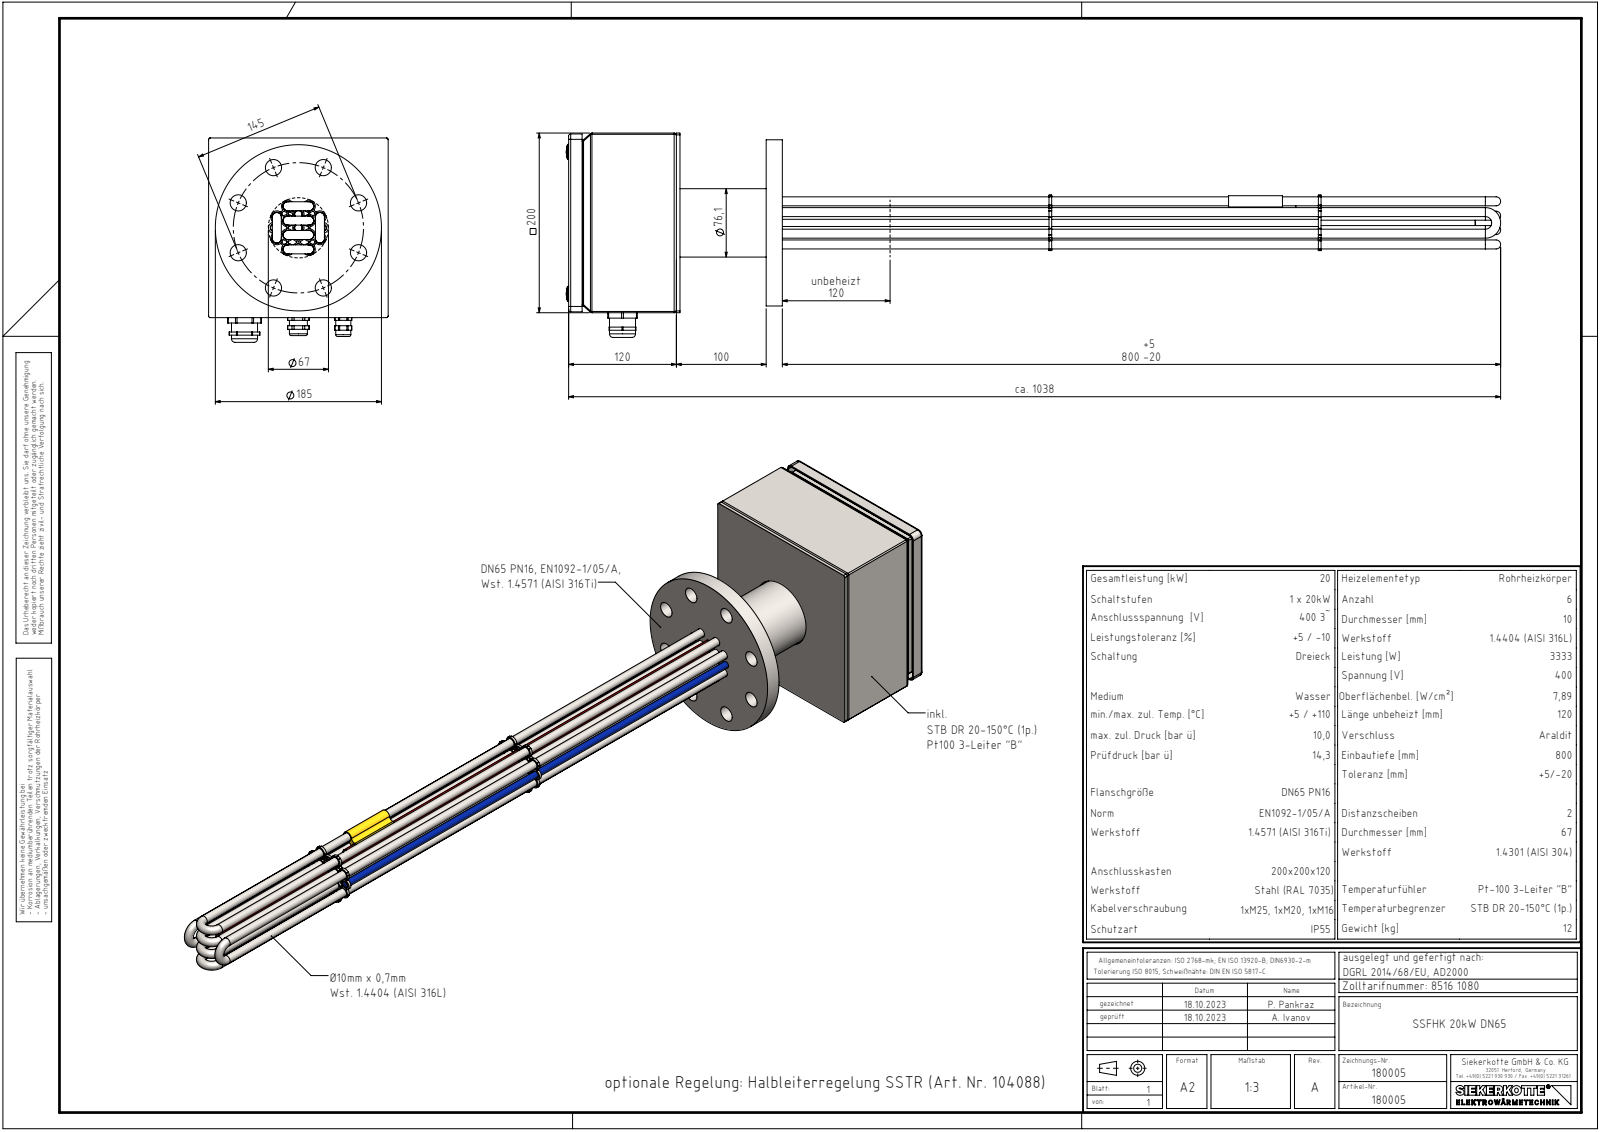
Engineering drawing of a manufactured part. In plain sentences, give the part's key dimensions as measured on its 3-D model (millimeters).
The part is named "BODY^AK 200x200x120_Anschlusskasten_SSFHK; Anschlusskasten^SSFHK_200x200x120; WB 10er^Fühlerschutzrohre_SSFHK; Kühlstrecke^SSFHK_DN80 (+8 more)". Its 3-D file was written by "SolidWorks 2021 (AUTOMOTIVE_DESIGN)". It is 31 solids with 1686 faces: 428 planar, 954 cylindrical and 304 other. Overall it measures 1040.75 by 227.5 by 200 millimeters. Its volume is 1 275 000 cubic millimeters and its surface area 1 234 000 square millimeters. Round holes: 16 of diameter 10.2, 12 of diameter 5, 12 of diameter 8, 12 of diameter 10.7, 9 of diameter 18, 4 of diameter 8.4, 4 of diameter 8.7, 3 of diameter 8.5, 2 of diameter 7, 2 of diameter 9.2, 2 of diameter 9.7, 1 of diameter 6.2. Round bosses or shafts: 16 of diameter 10, 6 of diameter 8, 4 of diameter 9.4, 4 of diameter 5.3, 4 of diameter 5, 4 of diameter 4.3, 4 of diameter 2.7, 2 of diameter 9. Partial cylindrical surfaces (rounded edges, fillets, slot ends): 124 of radius 0.5, 24 of radius 1.25, 24 of radius 2.5, 16 of radius 4.5, 12 of radius 6.85, 8 of radius 5, 6 of radius 2, 6 of radius 2.25. The main face-to-face distances are 1.25, 198.75, 118.75, 200, 120, 197.5, 124, 4, 122.75, 118. The hole center spacings are 26.83, 37.95, 45.77, 53.86, 55.11, 58.54, 72.5, 75.5.
